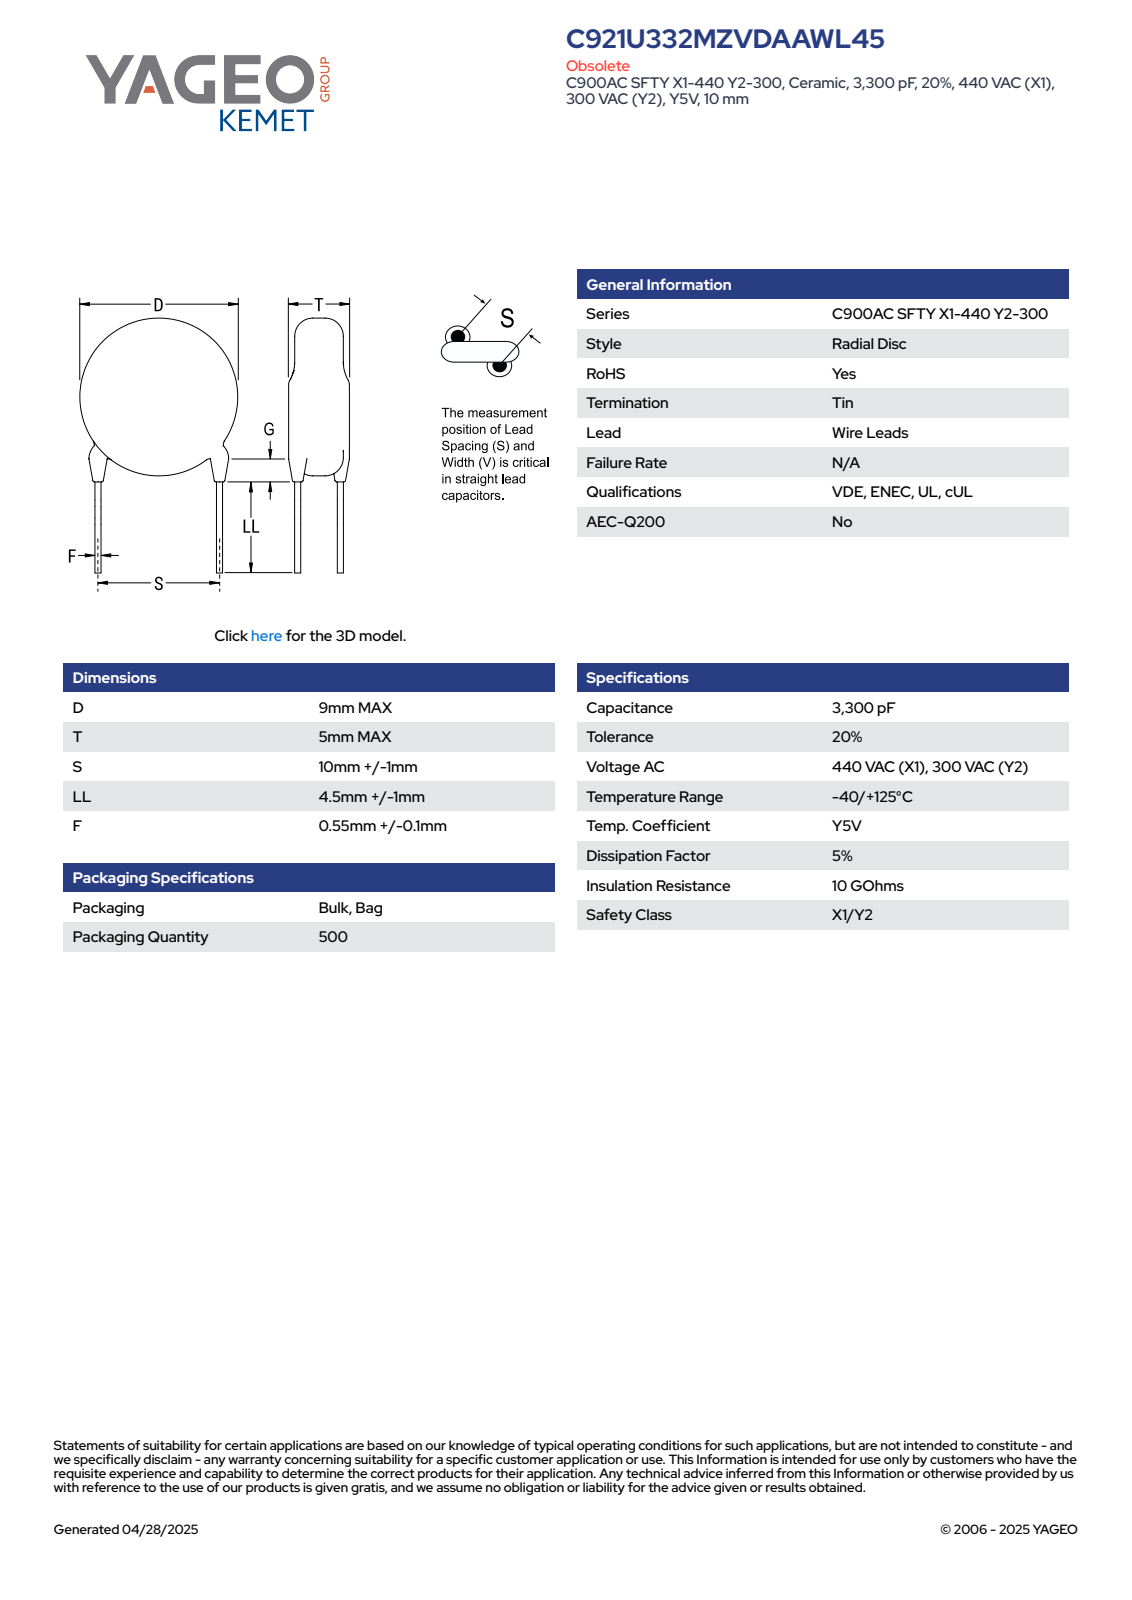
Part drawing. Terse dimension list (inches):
name: CCD_STC900_D9T5S10LL5.5F0.65G3
written by: SolidWorks 2014 (AUTOMOTIVE_DESIGN)
unit: in
bodies: 4 solids, 83 faces (61 planar, 6 cylindrical, 16 other)
size: 0.586 × 0.406 × 0.197
volume: 0.019 in³; area: 0.445 in²
bosses: 2× ⌀0.026, 1× ⌀0.354
face distances: 0.197, 0.041, 0.43, 0.389, 0.033, 0.018, 0.015, 0.084, 0.121, 0.126
